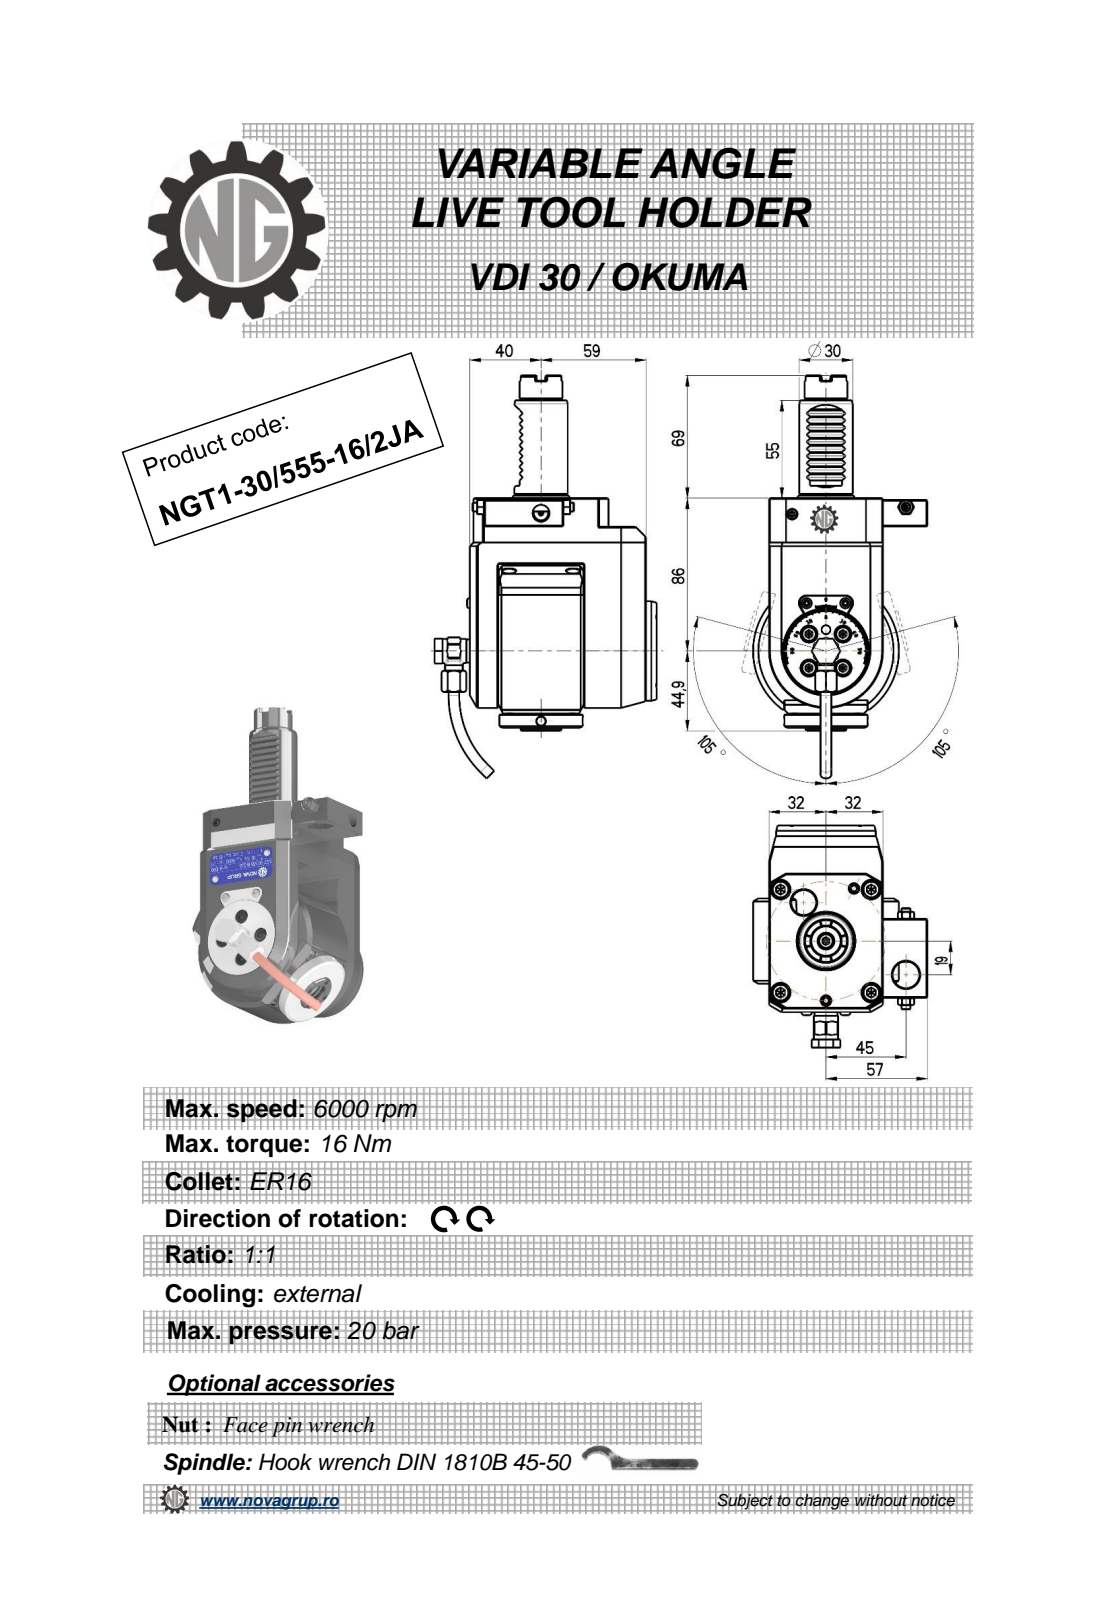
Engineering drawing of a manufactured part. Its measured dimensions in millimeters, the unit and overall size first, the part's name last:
Units: millimetres
Overall size (bounding box): 226.67 × 124.9 × 98
Round holes (diameter × count): ⌀3.2 ×4, ⌀4 ×3, ⌀5 ×2, ⌀3 ×1, ⌀4.2 ×1, ⌀6 ×1, ⌀6.2 ×1, ⌀9 ×1, ⌀9.5 ×1, ⌀11 ×1, ⌀12.5 ×1, ⌀15 ×1
Round bosses / shafts (diameter × count): ⌀10 ×2, ⌀6 ×2, ⌀5.7 ×2, ⌀56 ×1, ⌀47 ×1, ⌀36 ×1, ⌀30 ×1, ⌀24 ×1
Partial cylindrical surfaces — rounded edges, fillets, slot ends (radius × count): R0.26 ×12, R0.3 ×10, R0.16 ×6, R0.5 ×4, R1 ×2, R7.7 ×1, R32 ×1, R41 ×1
Main face-to-face distances: 64, 16, 37, 6, 21, 99, 105, 89, 14, 62
Hole centre spacings: 9.25, 13.08, 18.5, 49.87, 50.26, 0.4, 39.45, 39.75
Volume: 788 541 mm³ · Surface area: 75 034 mm²
Bodies: 1 solid, 570 faces (240 planar, 144 cylindrical, 186 other)
Part name (STEP PRODUCT): NGT1_30_555_16_2JA
STEP written by: PRO/ENGINEER BY PARAMETRIC TECHNOLOGY CORPORATION, 2010280 (CONFIG_CONTROL_DESIGN)
